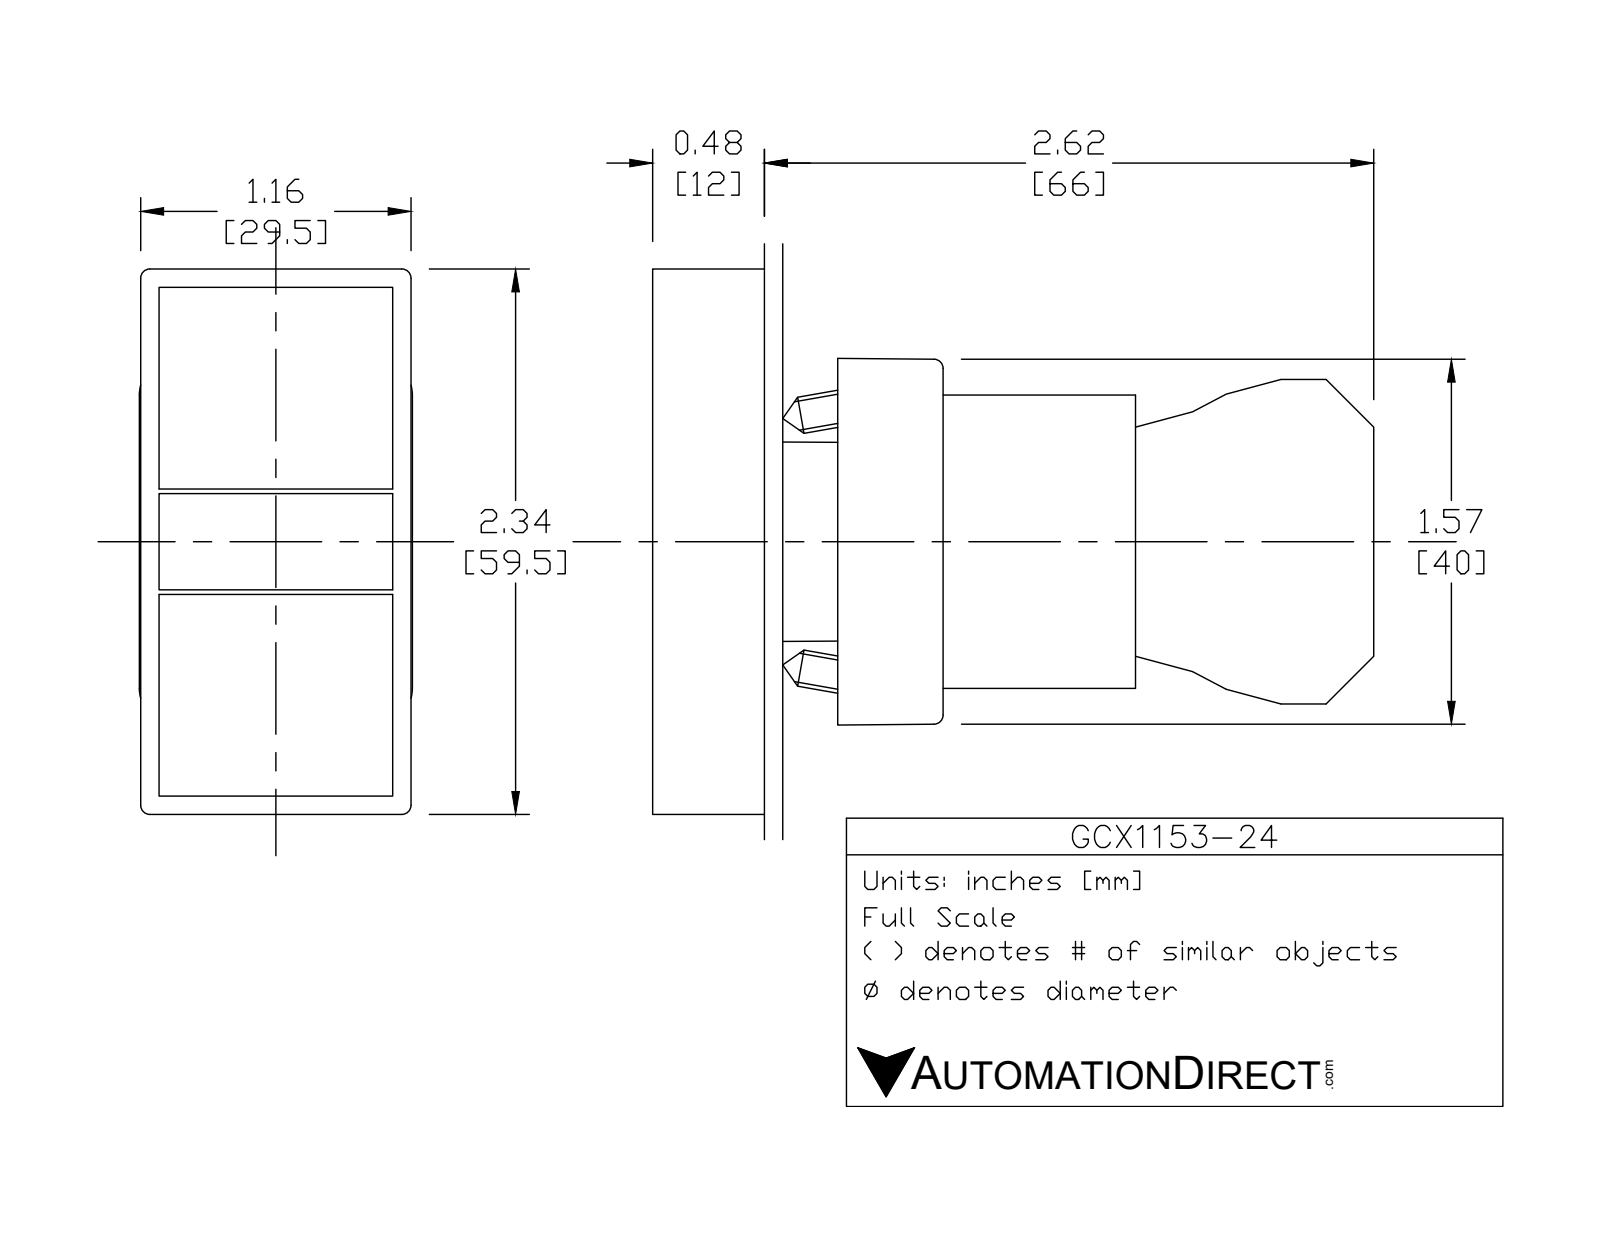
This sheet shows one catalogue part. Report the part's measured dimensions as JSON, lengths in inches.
{"part_name": "ecx1029; ECX1050; ecx1030; ecx1040 (+2 more)", "step_written_by": "SolidWorks 2016 (AUTOMOTIVE_DESIGN)", "units": "inches", "bodies": {"solids": 9, "faces": 542, "planar": 355, "cylindrical": 156, "other": 31}, "overall_size": [3.043, 2.343, 1.177], "volume_in3": 4.278, "surface_area_in2": 55.88, "round_holes": [[0.079, 4], [0.087, 2], [0.124, 2], [0.13, 2], [0.197, 1], [0.469, 1], [0.709, 1], [0.878, 1], [0.888, 1]], "round_bosses_or_shafts": [[0.157, 4], [0.945, 1], [0.856, 1], [0.78, 1], [0.591, 1], [0.504, 1]], "partial_cylinders_radius": [[0.059, 24], [0.041, 12], [0.124, 12], [0.157, 12], [0.039, 8], [0.063, 2], [0.079, 2], [0.128, 2]], "face_to_face_distances": [0.039, 0.02, 0.059, 0.579, 0.593, 0.74, 1.193, 0.453, 0.827, 1.567], "hole_center_spacings": [0.236, 1.003, 0.974, 0.472, 0.539, 0.544, 1.083, 0.484]}
